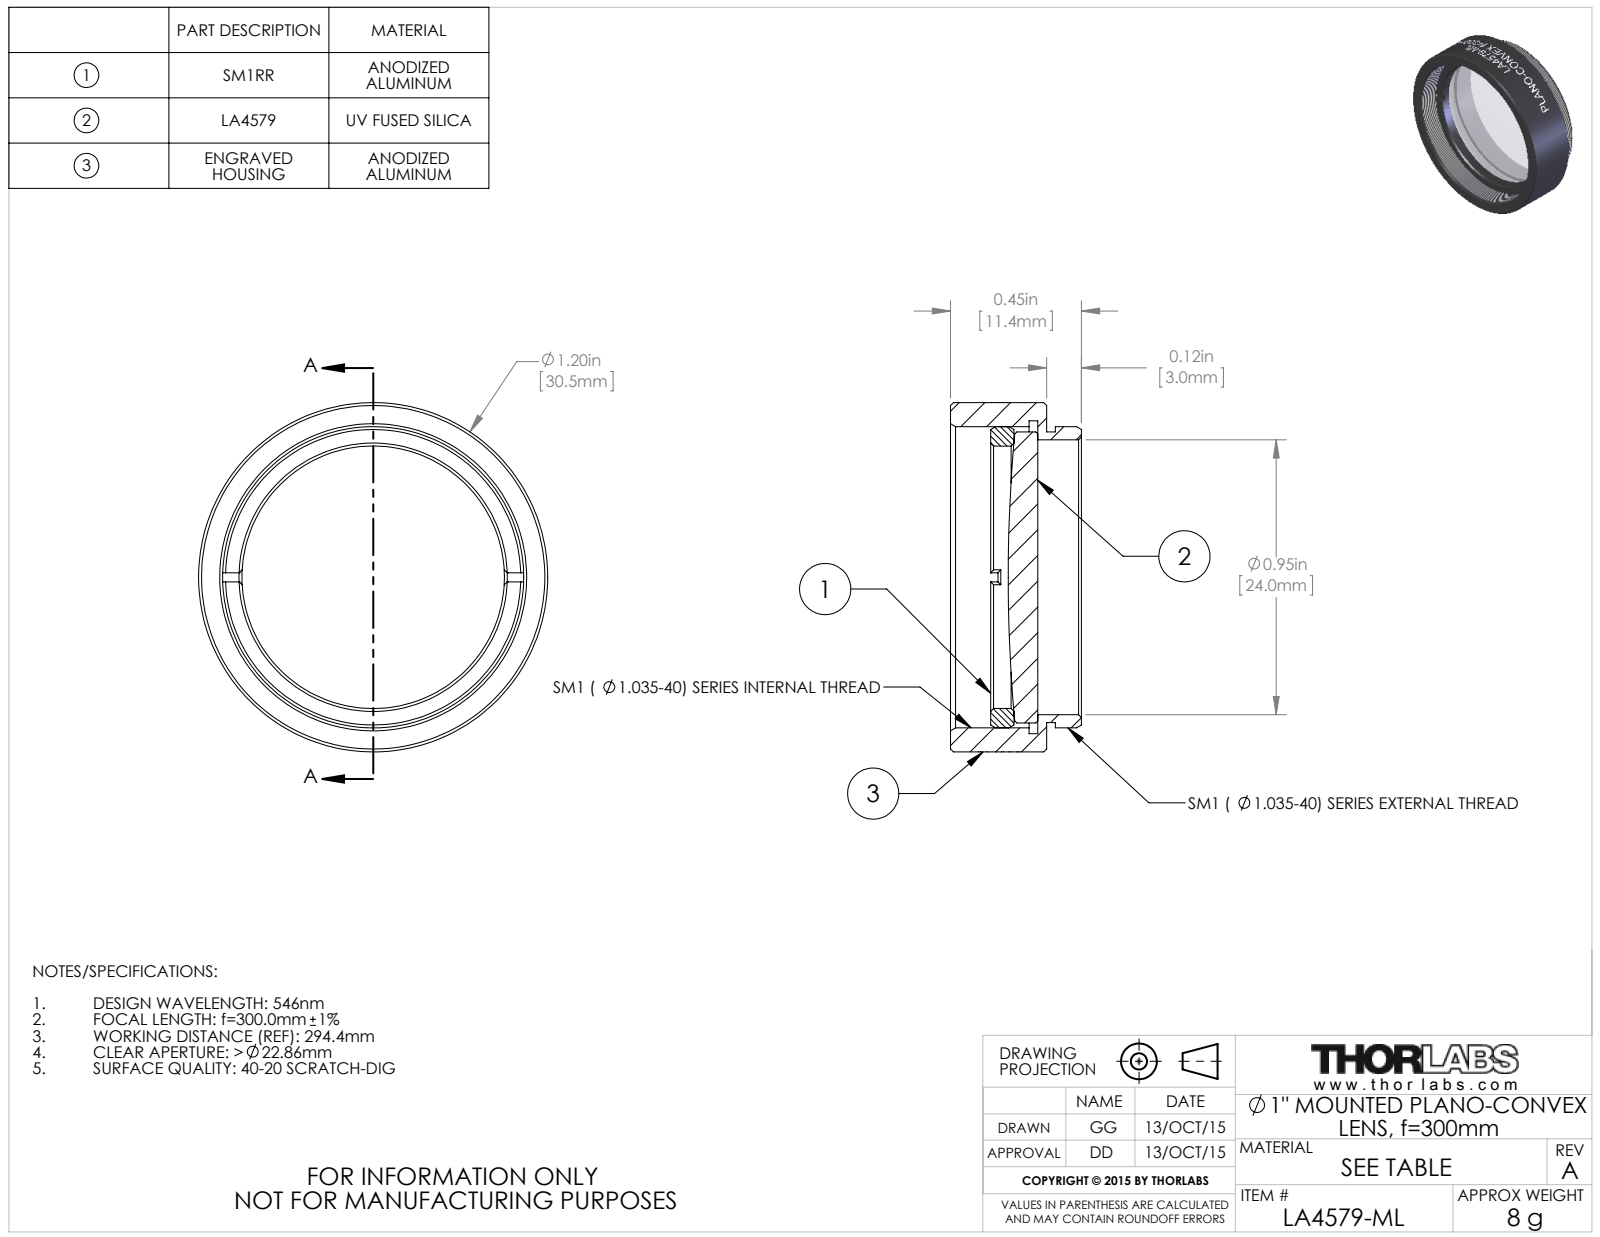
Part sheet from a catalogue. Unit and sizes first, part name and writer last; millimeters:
Units: millimetres
Overall size (bounding box): 30.48 × 30.48 × 11.43
Round holes (diameter × count): ⌀22.91 ×1, ⌀24 ×1, ⌀27.31 ×1
Round bosses / shafts (diameter × count): ⌀30.48 ×1, ⌀26.29 ×1, ⌀25.4 ×1, ⌀25.37 ×1
Main face-to-face distances: 0.76, 8.38, 7.62, 2.85, 2.09, 5.53, 4.88, 4.12, 2.03, 3.5
Volume: 3 242 mm³ · Surface area: 4 298 mm²
Bodies: 3 solids, 127 faces (20 planar, 79 cylindrical, 28 other)
Part name (STEP PRODUCT): TTN039309-E0W
STEP written by: SolidWorks 2014 (CONFIG_CONTROL_DESIGN)
